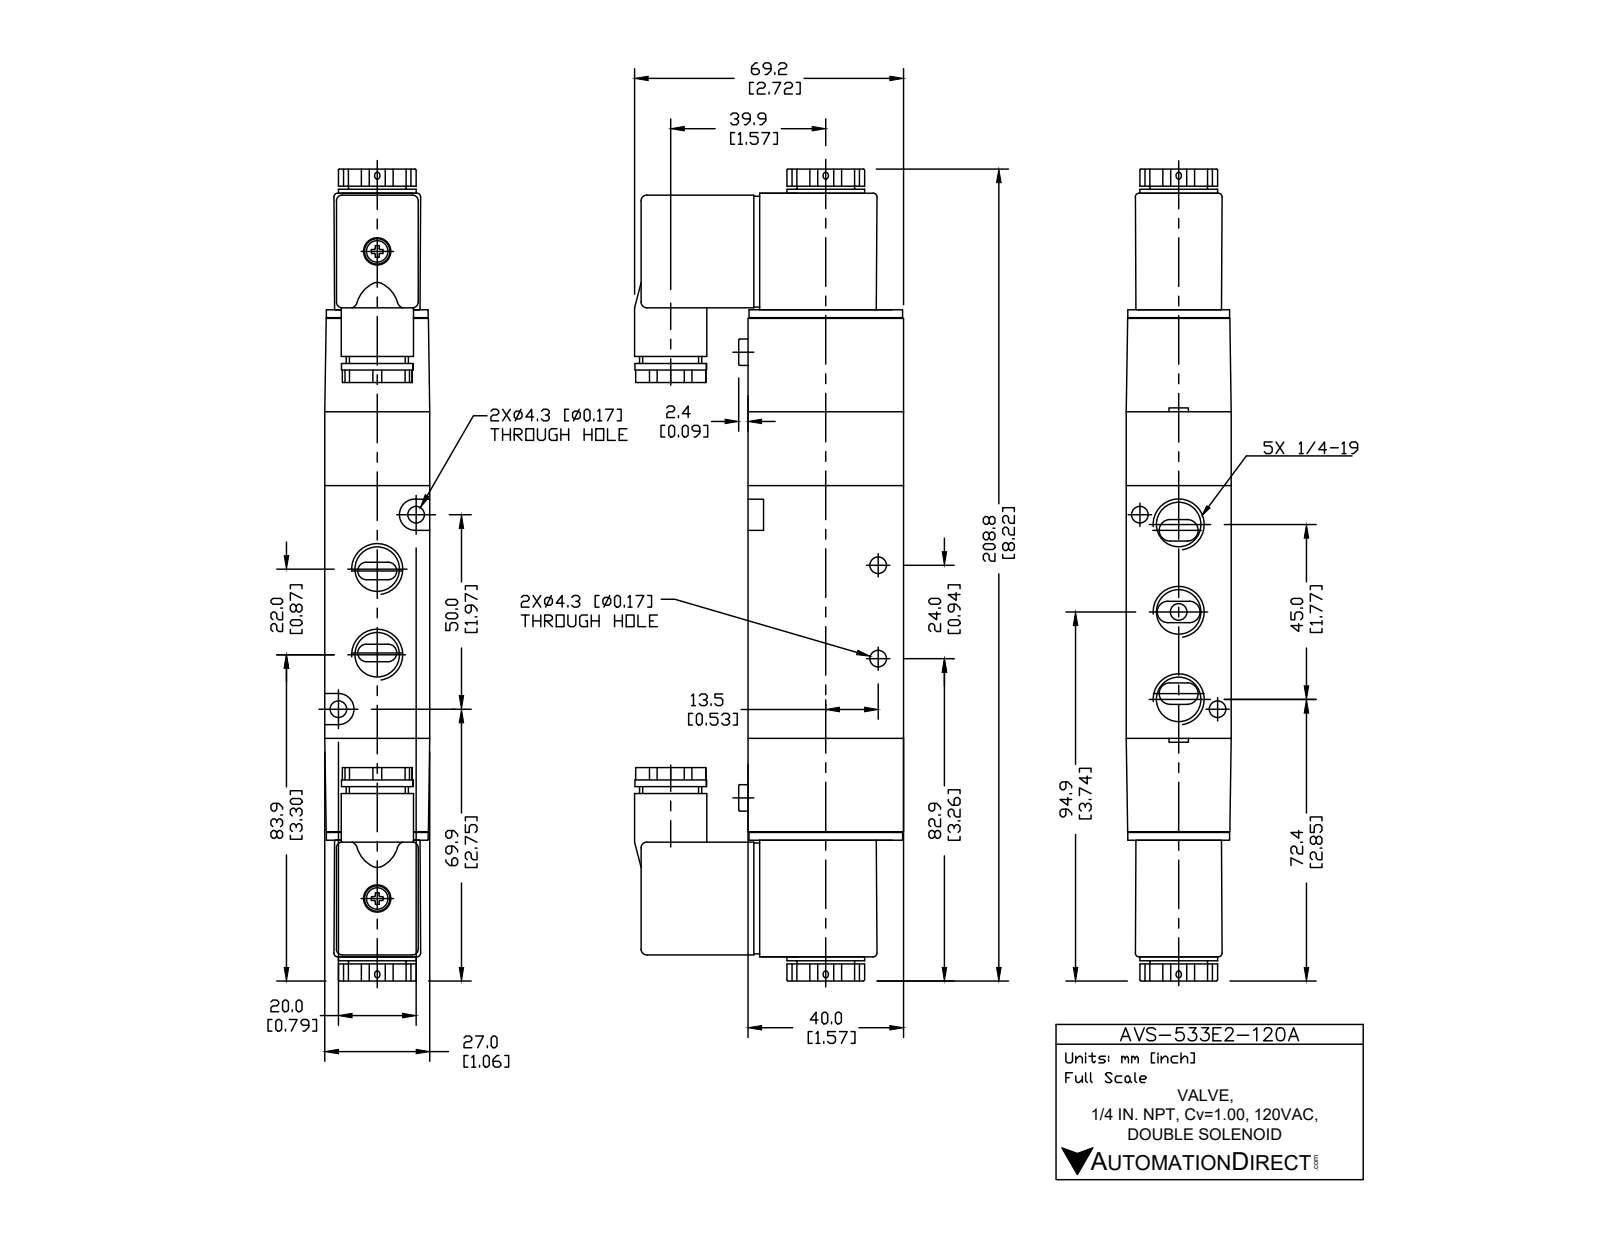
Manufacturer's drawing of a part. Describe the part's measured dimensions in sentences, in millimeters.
The part is named "AVS-533E2-120A". Its 3-D file was written by "SolidWorks 2015 (CONFIG_CONTROL_DESIGN)". It is 5 solids with 278 faces: 133 planar, 111 cylindrical and 34 other. Overall it measures 208.8 by 69.2 by 27 millimeters. Its volume is 224 505 cubic millimeters and its surface area 45 623 square millimeters. Round holes: 5 of diameter 11.13, 4 of diameter 4.3, 1 of diameter 9.3. Round bosses or shafts: 2 of diameter 6.7, 1 of diameter 20, 1 of diameter 18.6, 1 of diameter 18.4, 1 of diameter 16, 1 of diameter 14.8. Partial cylindrical surfaces (rounded edges, fillets, slot ends): 18 of radius 1.5, 12 of radius 3, 10 of radius 1, 8 of radius 0.5. The main face-to-face distances are 27, 3, 24, 40, 84, 23.22, 21, 29.5, 0.5, 166.4. The hole center spacings are 10.31, 11, 11.5, 17.2, 22.5, 26.93, 33.5, 37.36.
